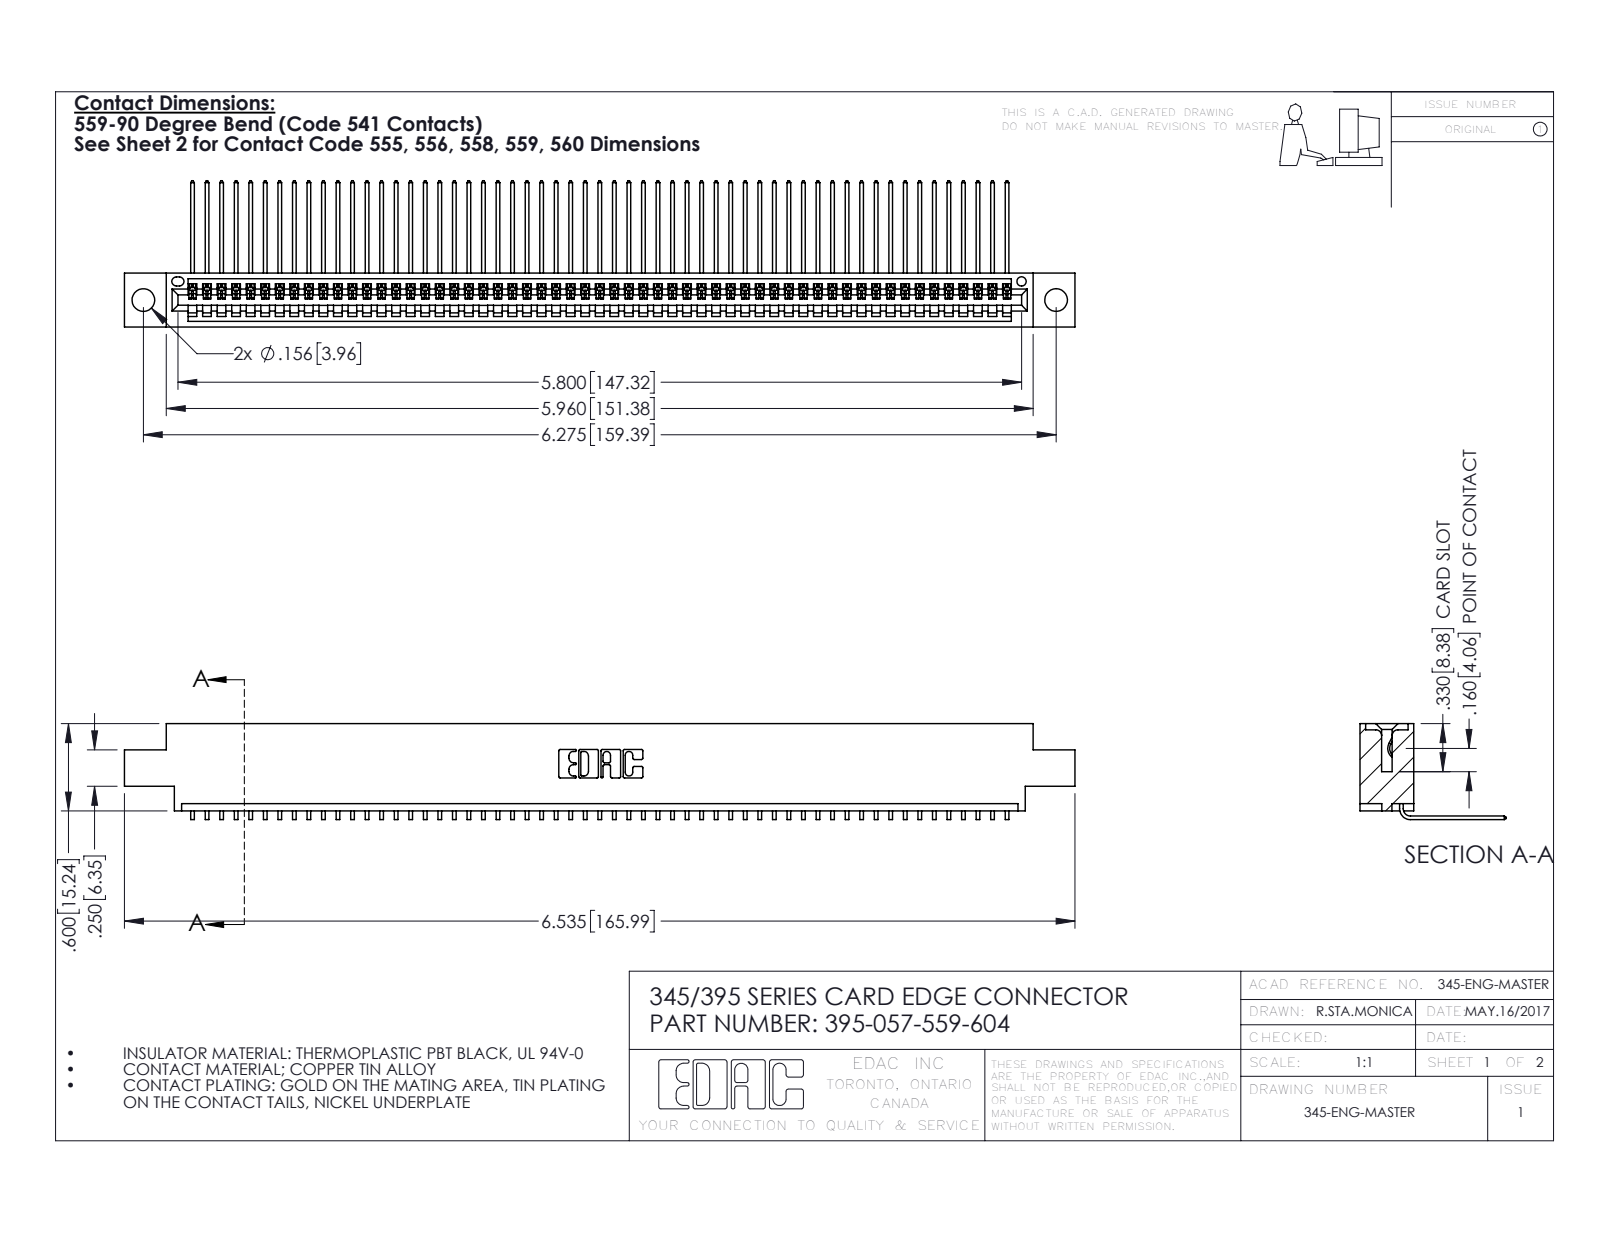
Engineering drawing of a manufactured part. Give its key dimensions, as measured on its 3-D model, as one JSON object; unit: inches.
{"part_name": "345-292-001_558 559 Tail - 1; 395-057-559-604; 345 Part_0.170 Offset - 0.156 Dia-TH", "step_written_by": "SolidWorks 2016 (CONFIG_CONTROL_DESIGN)", "units": "inches", "bodies": {"solids": 58, "faces": 3550, "planar": 2478, "cylindrical": 1072, "other": 0}, "overall_size": [6.535, 1.005, 0.659], "volume_in3": 0.969, "surface_area_in2": 34.65, "round_holes": [[0.156, 2], [0.064, 1]], "partial_cylinders_radius": [[0.006, 114], [0.01, 22], [0.007, 6], [0.031, 6], [0.026, 3], [0.031, 2], [0.04, 2], [0.014, 1]], "face_to_face_distances": [0.072, 0.298, 0.37, 0.2, 0.098, 0.272, 0.025, 0.225, 0.175, 0.149], "hole_center_spacings": [0.27, 6.039, 6.275]}
